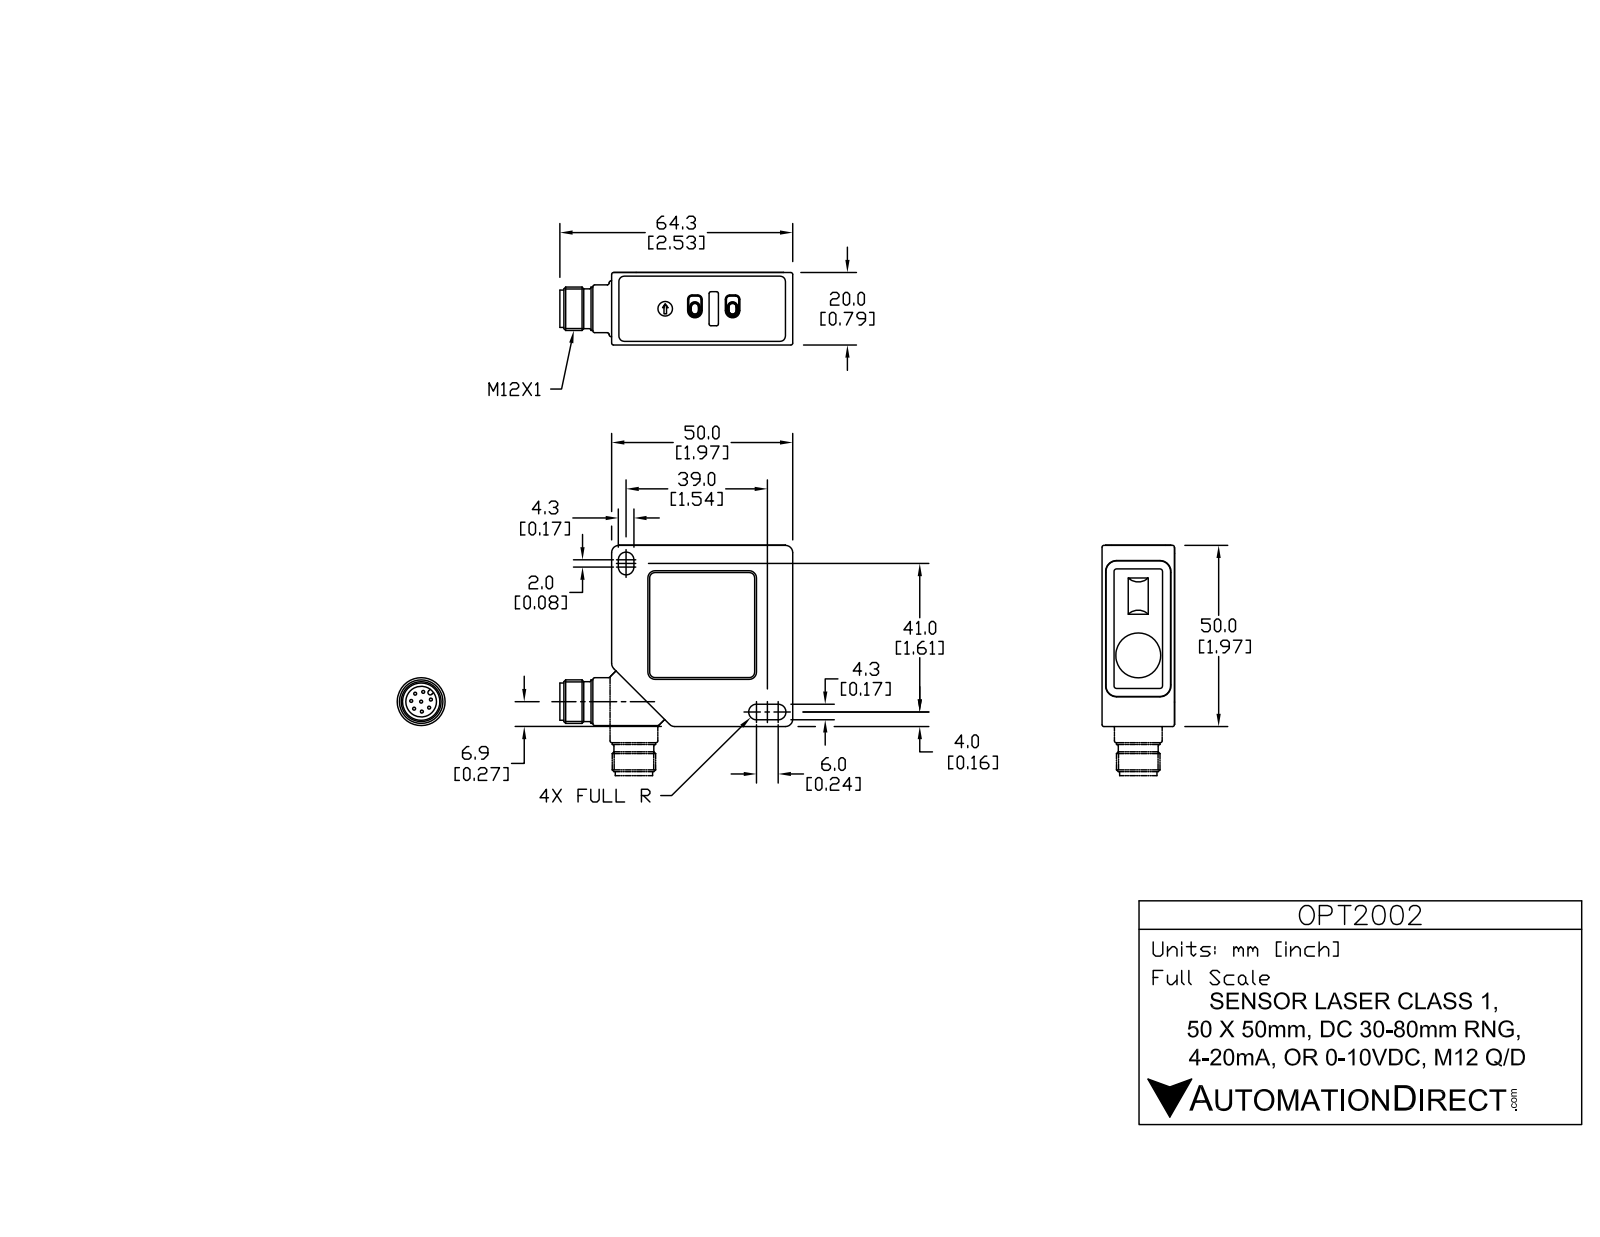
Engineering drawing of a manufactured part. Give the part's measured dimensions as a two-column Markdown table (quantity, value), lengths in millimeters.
| quantity | value |
| --- | --- |
| part name | OPT2002 |
| STEP written by | SolidWorks 2013 (AUTOMOTIVE_DESIGN) |
| units | millimeters |
| bodies | 15 solids, 301 faces (153 planar, 134 cylindrical, 14 other) |
| overall size | 64.43 × 50.1 × 20 |
| volume | 48 653 mm³ |
| surface area | 16 026 mm² |
| round holes (diameter × count) | 4 × 1, 8.45 × 1 |
| round bosses / shafts (diameter × count) | 0.82 × 8, 18 × 1, 13.5 × 1, 12.39 × 1, 12 × 1, 11 × 1, 10.3 × 1 |
| partial cylindrical surfaces (radius × count) | 2 × 17, 0.2 × 10, 1 × 8, 2.1 × 5, 0.5 × 4, 1.2 × 4, 2.15 × 4, 2.9 × 4 |
| main face-to-face distances | 20, 19.8, 50, 50.1, 48.3, 1.6, 48.4, 5.33, 53.63, 53.73 |
